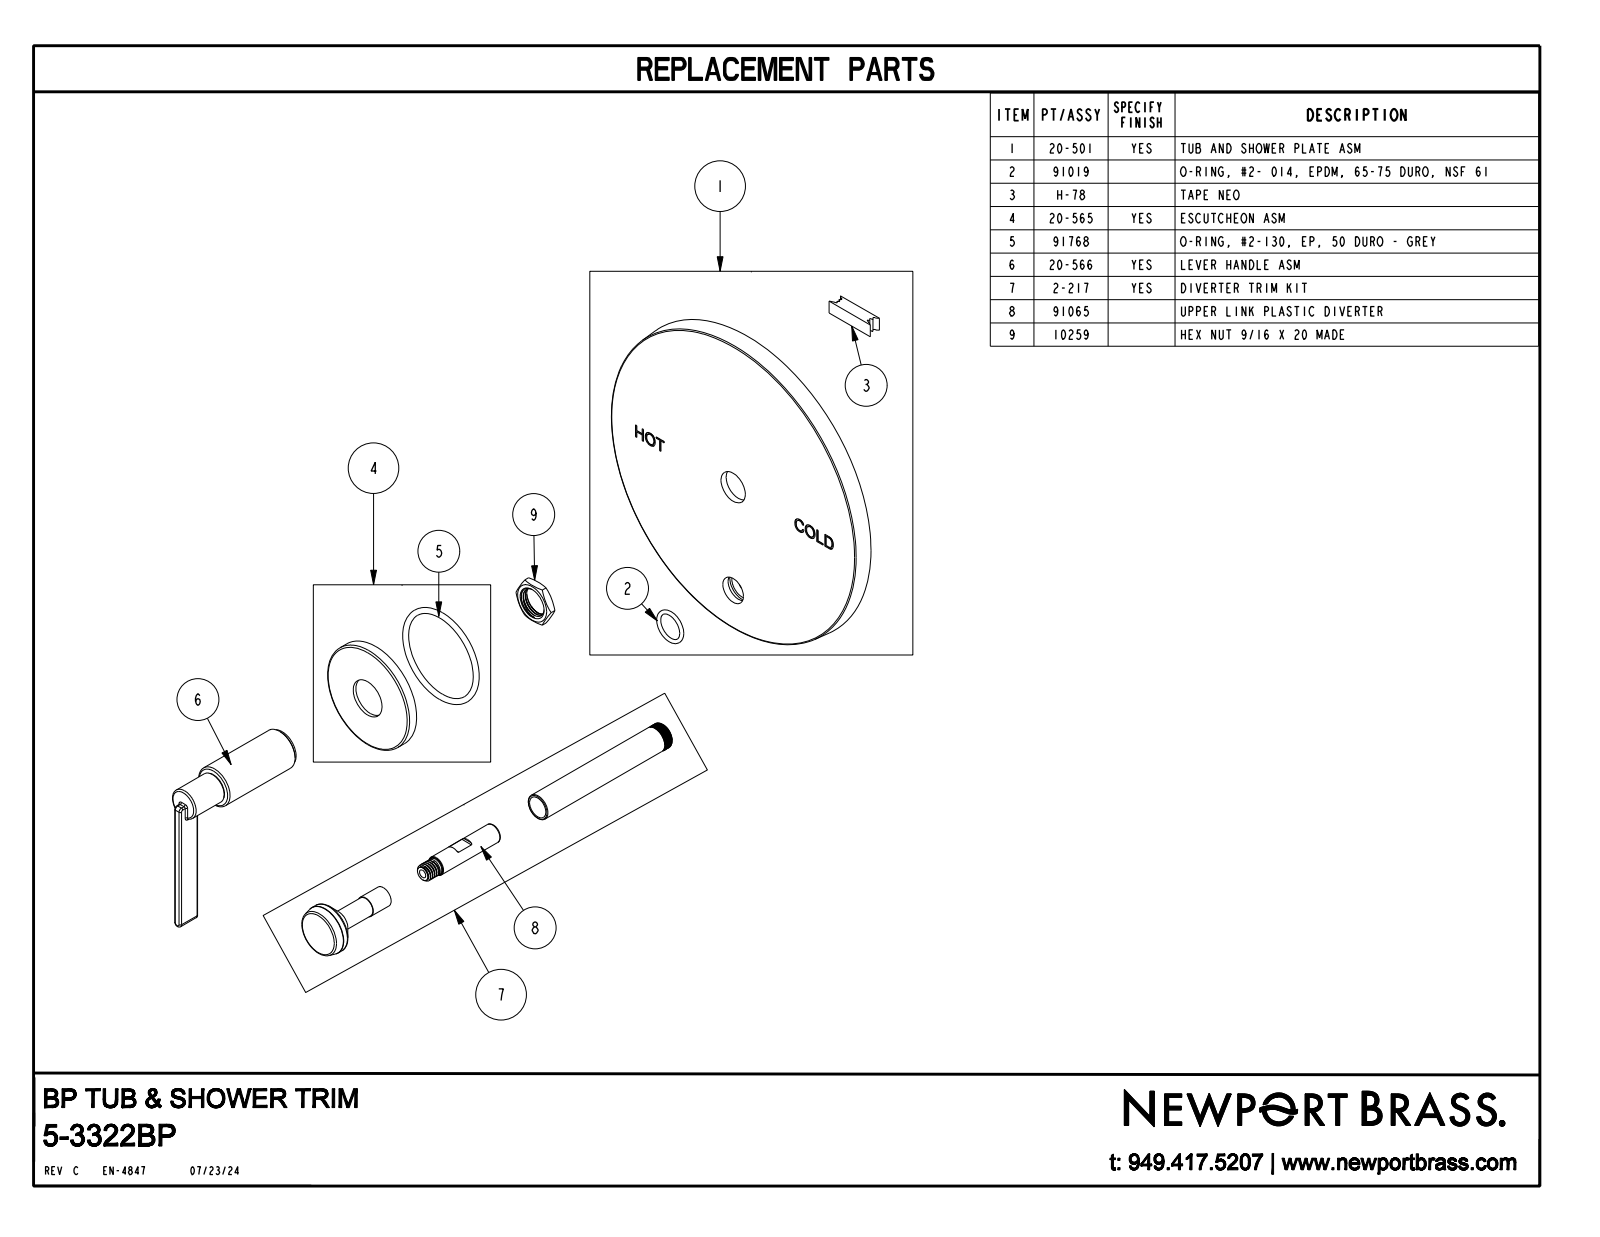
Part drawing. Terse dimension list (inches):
name: 30748; 20-501_ASM; 10497; 10496 (+8 more)
written by: CREO PARAMETRIC BY PTC INC, 2018400 (CONFIG_CONTROL_DESIGN)
unit: in
bodies: 7 solids, 479 faces (124 planar, 163 cylindrical, 192 other)
size: 6 × 5.994 × 5.501
volume: 5.398 in³; area: 102.2 in²
holes: 2× ⌀0.6, 1× ⌀0.11, 1× ⌀0.265, 1× ⌀0.318, 1× ⌀0.345, 1× ⌀0.36, 1× ⌀0.397, 1× ⌀0.4, 1× ⌀0.5, 1× ⌀0.516, 1× ⌀0.535, 1× ⌀0.59
bosses: 1× ⌀2, 1× ⌀1.65, 1× ⌀1, 1× ⌀0.9, 1× ⌀0.75, 1× ⌀0.73, 1× ⌀0.68, 1× ⌀0.563
rounds: 11× R0.03, 1× R0.06, 1× R0.075, 1× R0.137
face distances: 0.125, 0.225, 0.35, 0.55, 0.325, 0.2, 0.15, 0.05, 0.5, 0.275
hole spacings: 2.17
